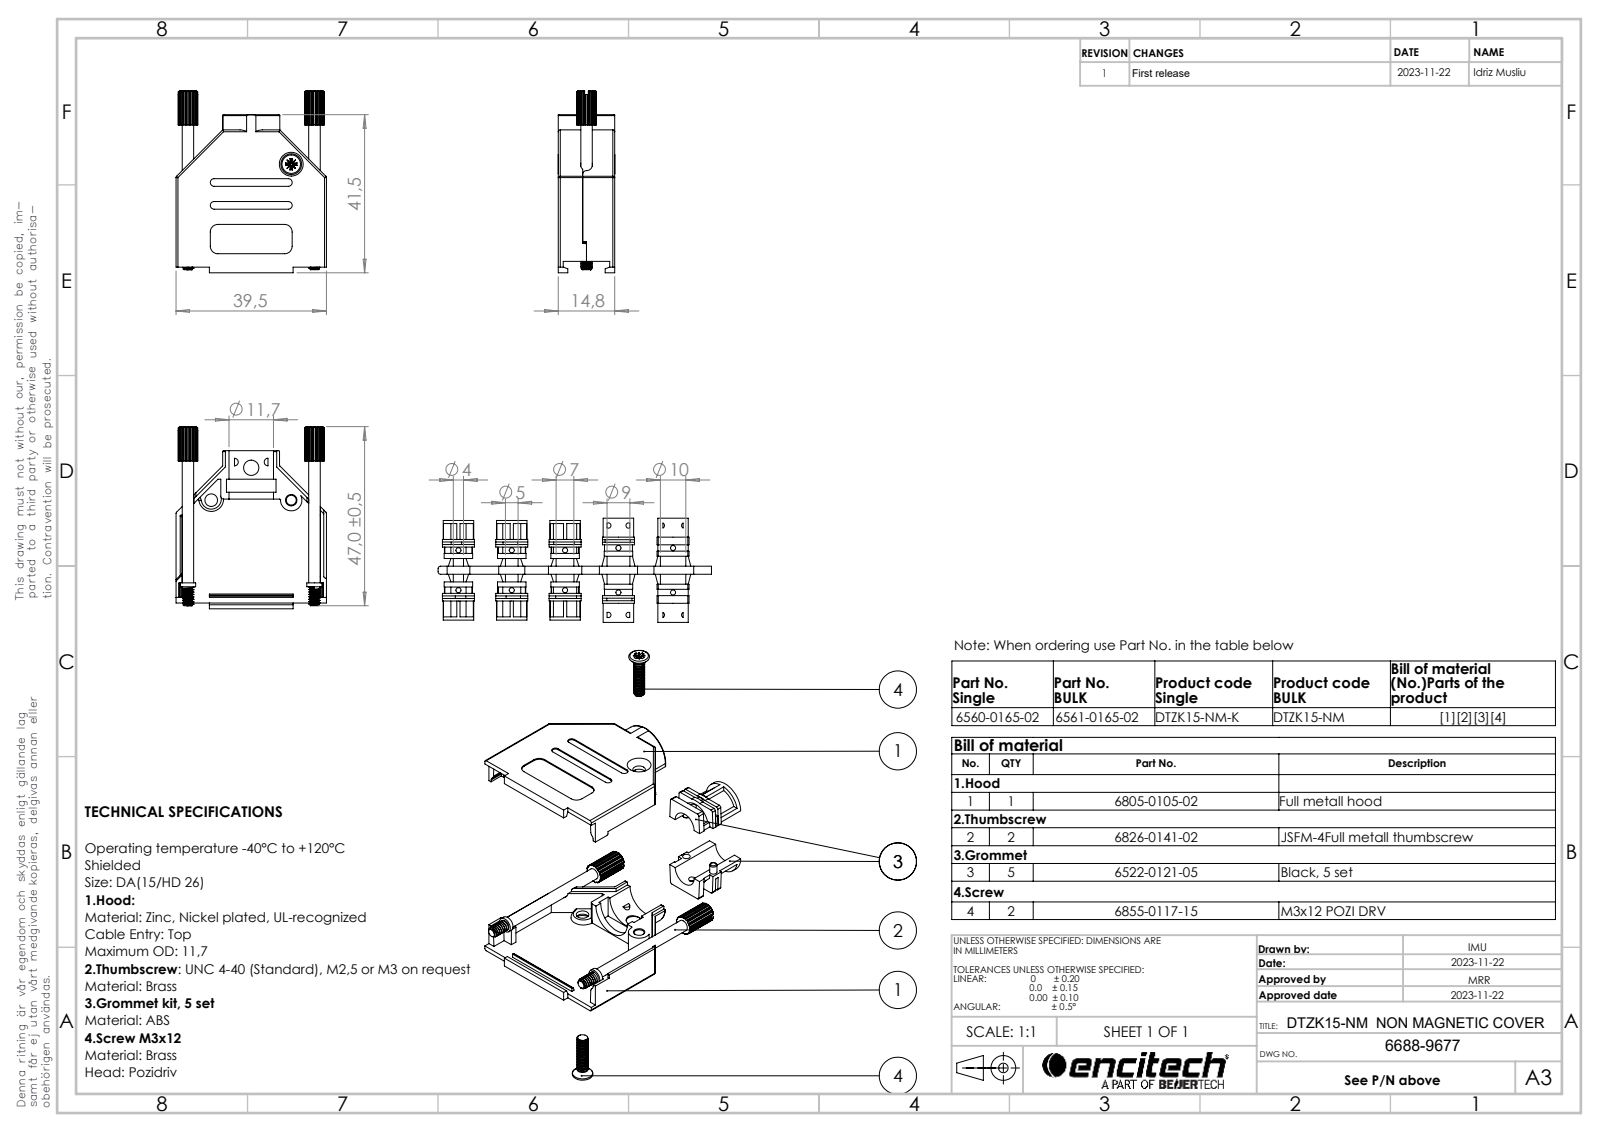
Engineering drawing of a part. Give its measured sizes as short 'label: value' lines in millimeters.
name: 6805-0105-02; 6855-0117-15; 6522-0121-05 (7mm); 6688-9677 (+1 more)
written by: SolidWorks 2021 (AUTOMOTIVE_DESIGN)
unit: mm
bodies: 8 solids, 782 faces (430 planar, 272 cylindrical, 80 other)
size: 47 × 39.5 × 14.95
volume: 7 857 mm³; area: 12 036 mm²
holes: 3× ⌀2, 2× ⌀2.6, 2× ⌀3.3, 1× ⌀4, 1× ⌀7, 1× ⌀11.7
bosses: 4× ⌀3, 2× ⌀4, 2× ⌀2.8, 2× ⌀1.9, 1× ⌀15, 1× ⌀11.6, 1× ⌀9.2
rounds: 24× R0.5, 12× R1, 8× R0.1, 8× R0.25, 6× R0.2, 4× R0.3, 4× R1.55, 4× R2
face distances: 1.3, 13.5, 14.8, 12.2, 6.1, 7.4, 1, 7.1, 1.6, 14.5
hole spacings: 5.71, 6.6, 6.97, 10.54, 13.51, 15.92, 7.6, 10
